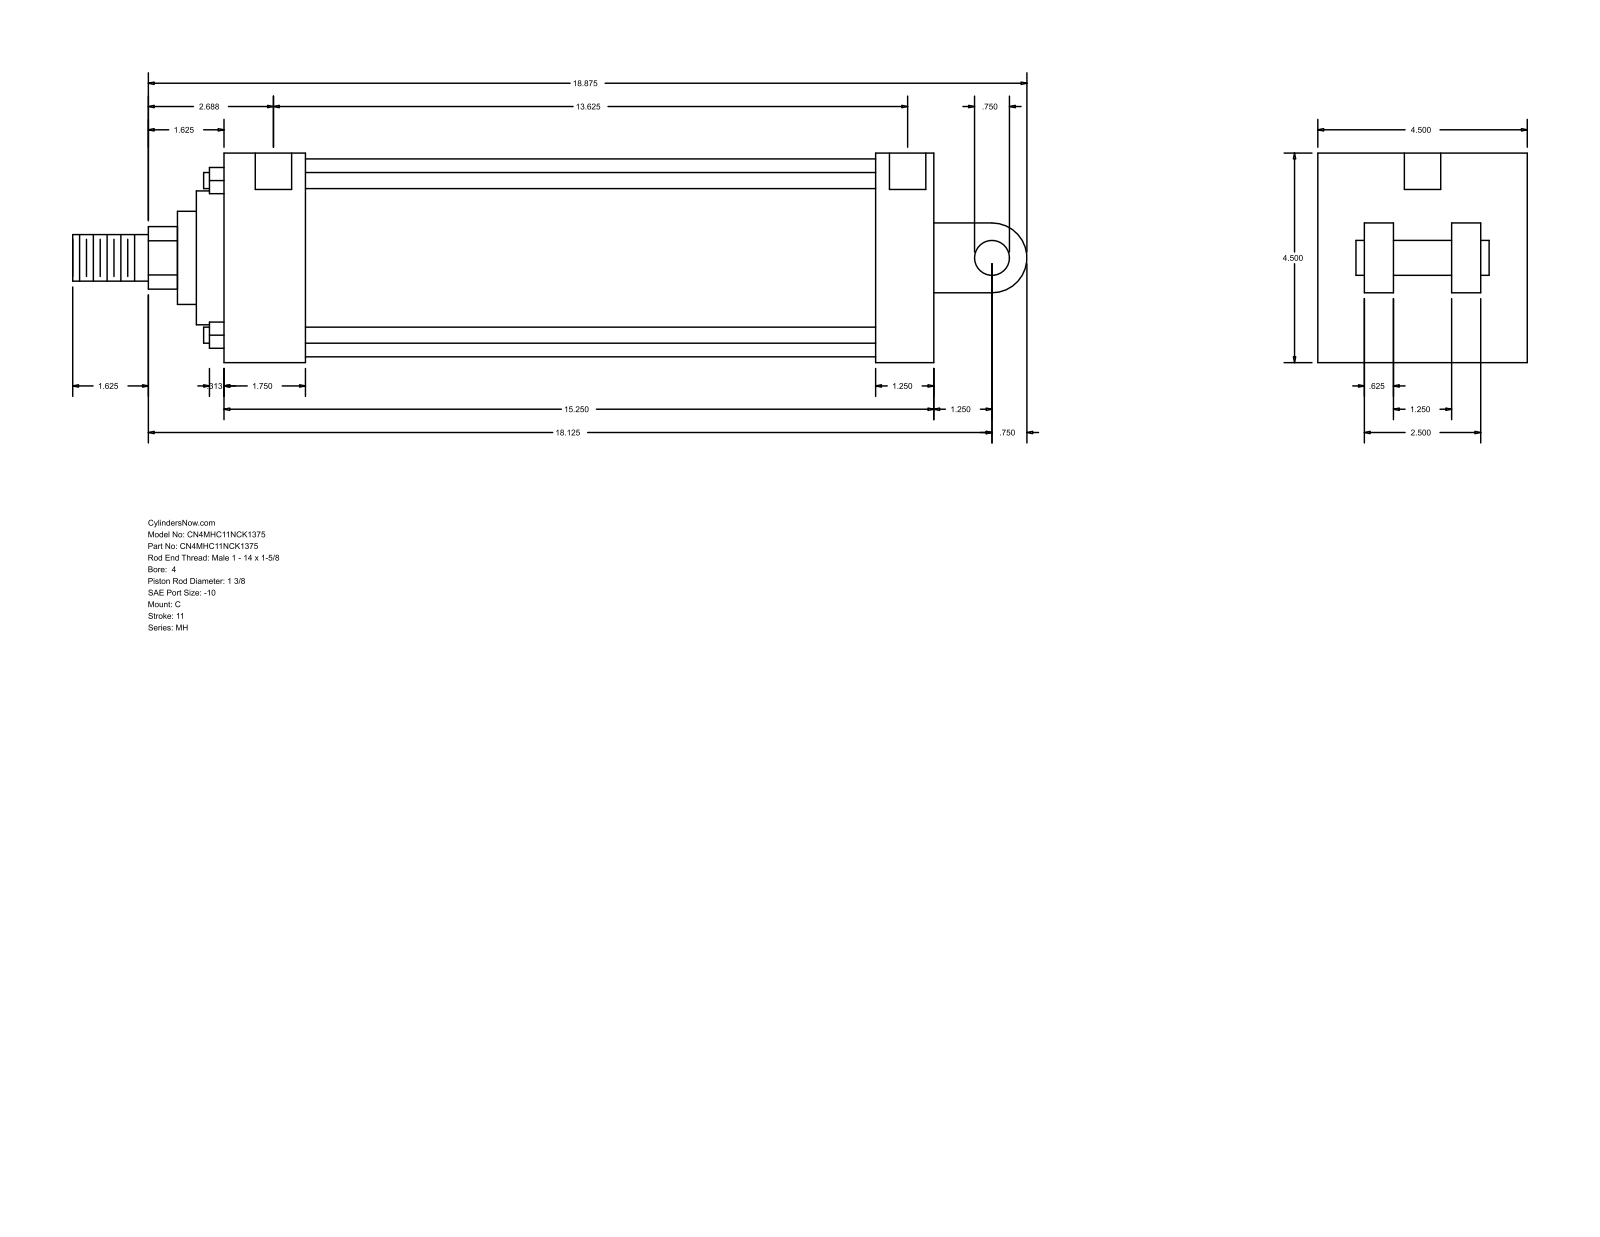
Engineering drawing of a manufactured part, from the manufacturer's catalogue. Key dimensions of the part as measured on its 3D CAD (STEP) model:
Part name (STEP PRODUCT): MH_C__0400_1.375
STEP written by: GSSL Pune (CONFIG_CONTROL_DESIGN)
Units: millimetres
Bodies: 0 solids, 101 faces (71 planar, 30 cylindrical, 0 other)
Overall size (bounding box): 520.7 × 114.3 × 114.3
Round holes (diameter × count): ⌀8.73 ×4, ⌀19.84 ×2
Round bosses / shafts (diameter × count): ⌀8.76 ×4, ⌀107.95 ×1, ⌀73.03 ×1, ⌀50.8 ×1, ⌀34.92 ×1, ⌀25.4 ×1, ⌀19.05 ×1
Partial cylindrical surfaces — rounded edges, fillets, slot ends (radius × count): R17.06 ×1, R19.05 ×1
Main face-to-face distances: 114.3, 387.35, 44.45, 355.61, 311.16, 342.9, 31.74, 41.27, 73.03, 38.1
Hole centre spacings: 1.59, 347.67, 349.26, 346.08
